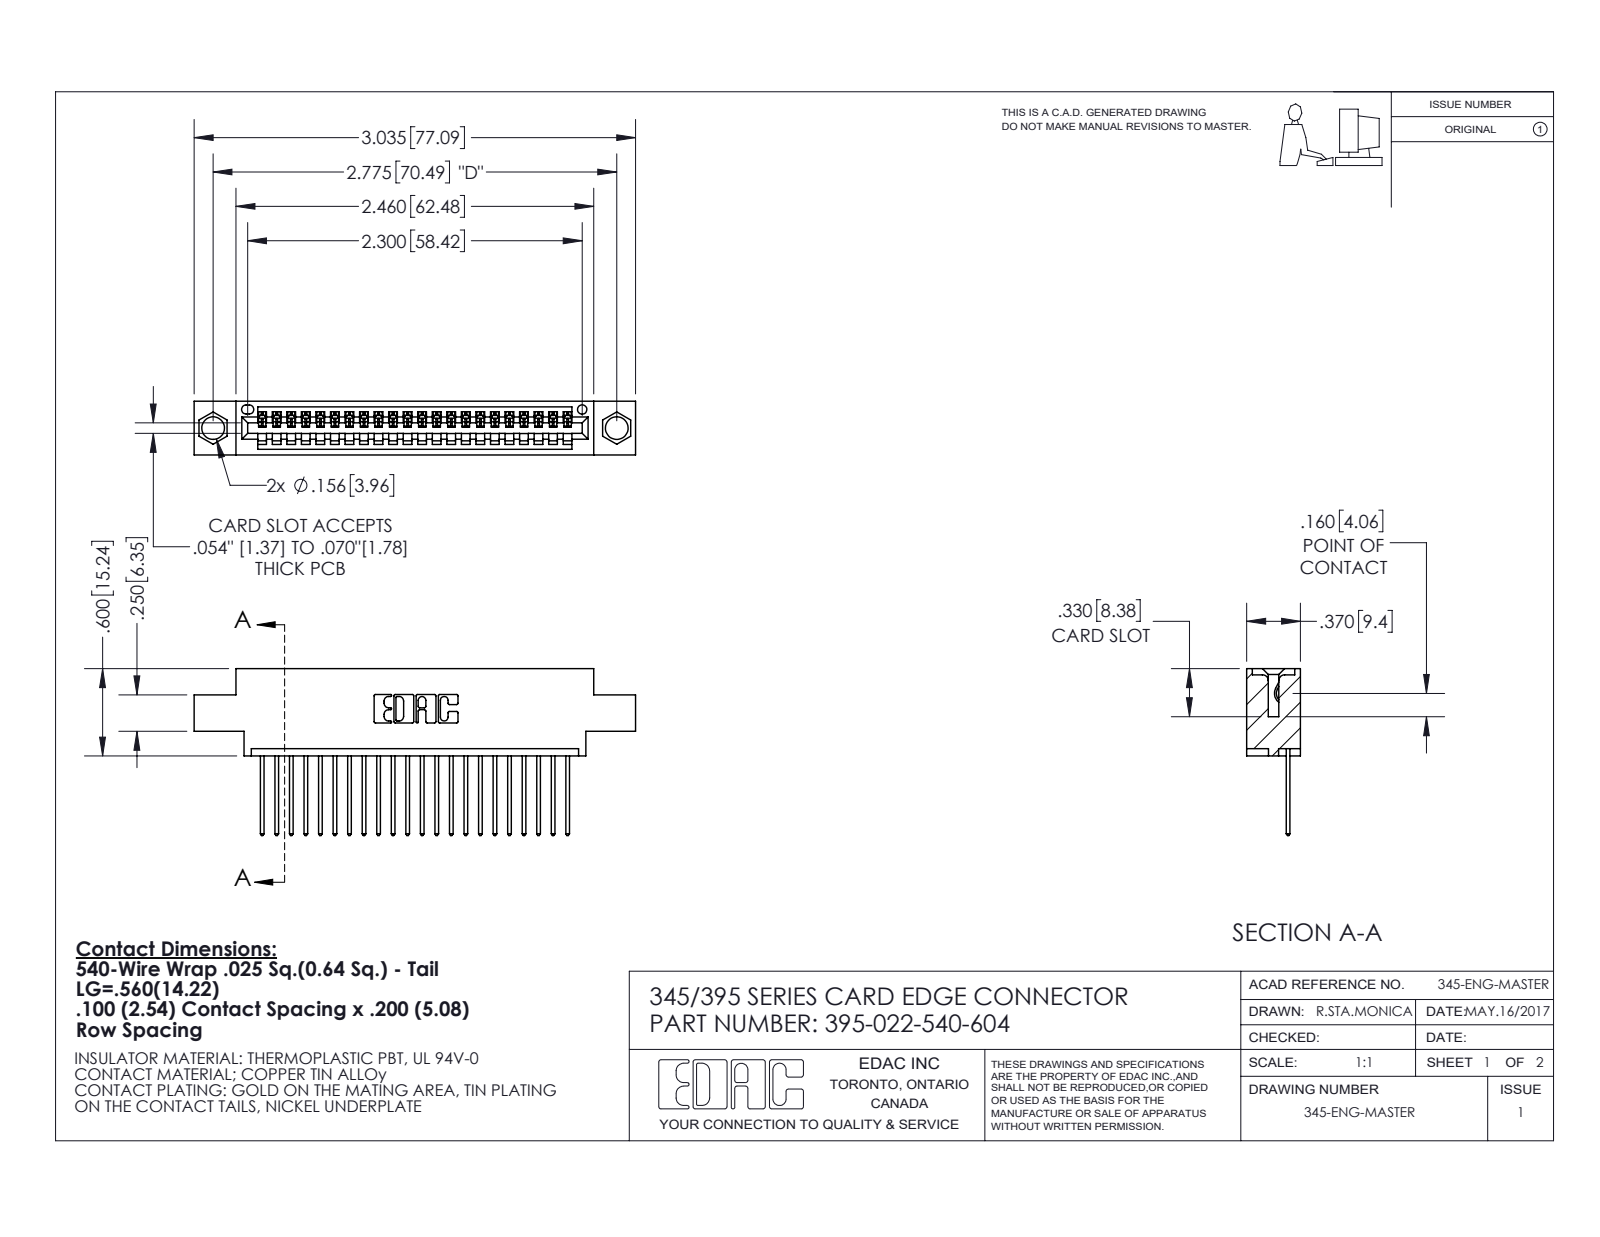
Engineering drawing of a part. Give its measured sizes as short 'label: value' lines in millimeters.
name: 345 Part_0.170 Offset - 0.156 Dia-TI; 345-292-001_345-293-140; 395-022-540-604
written by: SolidWorks 2020 (CONFIG_CONTROL_DESIGN)
unit: mm
bodies: 23 solids, 1420 faces (978 planar, 442 cylindrical, 0 other)
size: 77.1 × 29.1 × 9.4
volume: 6 960 mm³; area: 9 174 mm²
holes: 2× ⌀4, 1× ⌀1.6
rounds: 44× R0.2, 44× R0.3, 22× R0.3, 6× R0.2, 6× R0.8, 3× R0.7, 2× R0.8, 2× R1
face distances: 1.8, 7.6, 9.4, 5.1, 2.5, 6.9, 0.6, 5.7, 4.4, 3.8
hole spacings: 6.9, 64.5, 70.5
